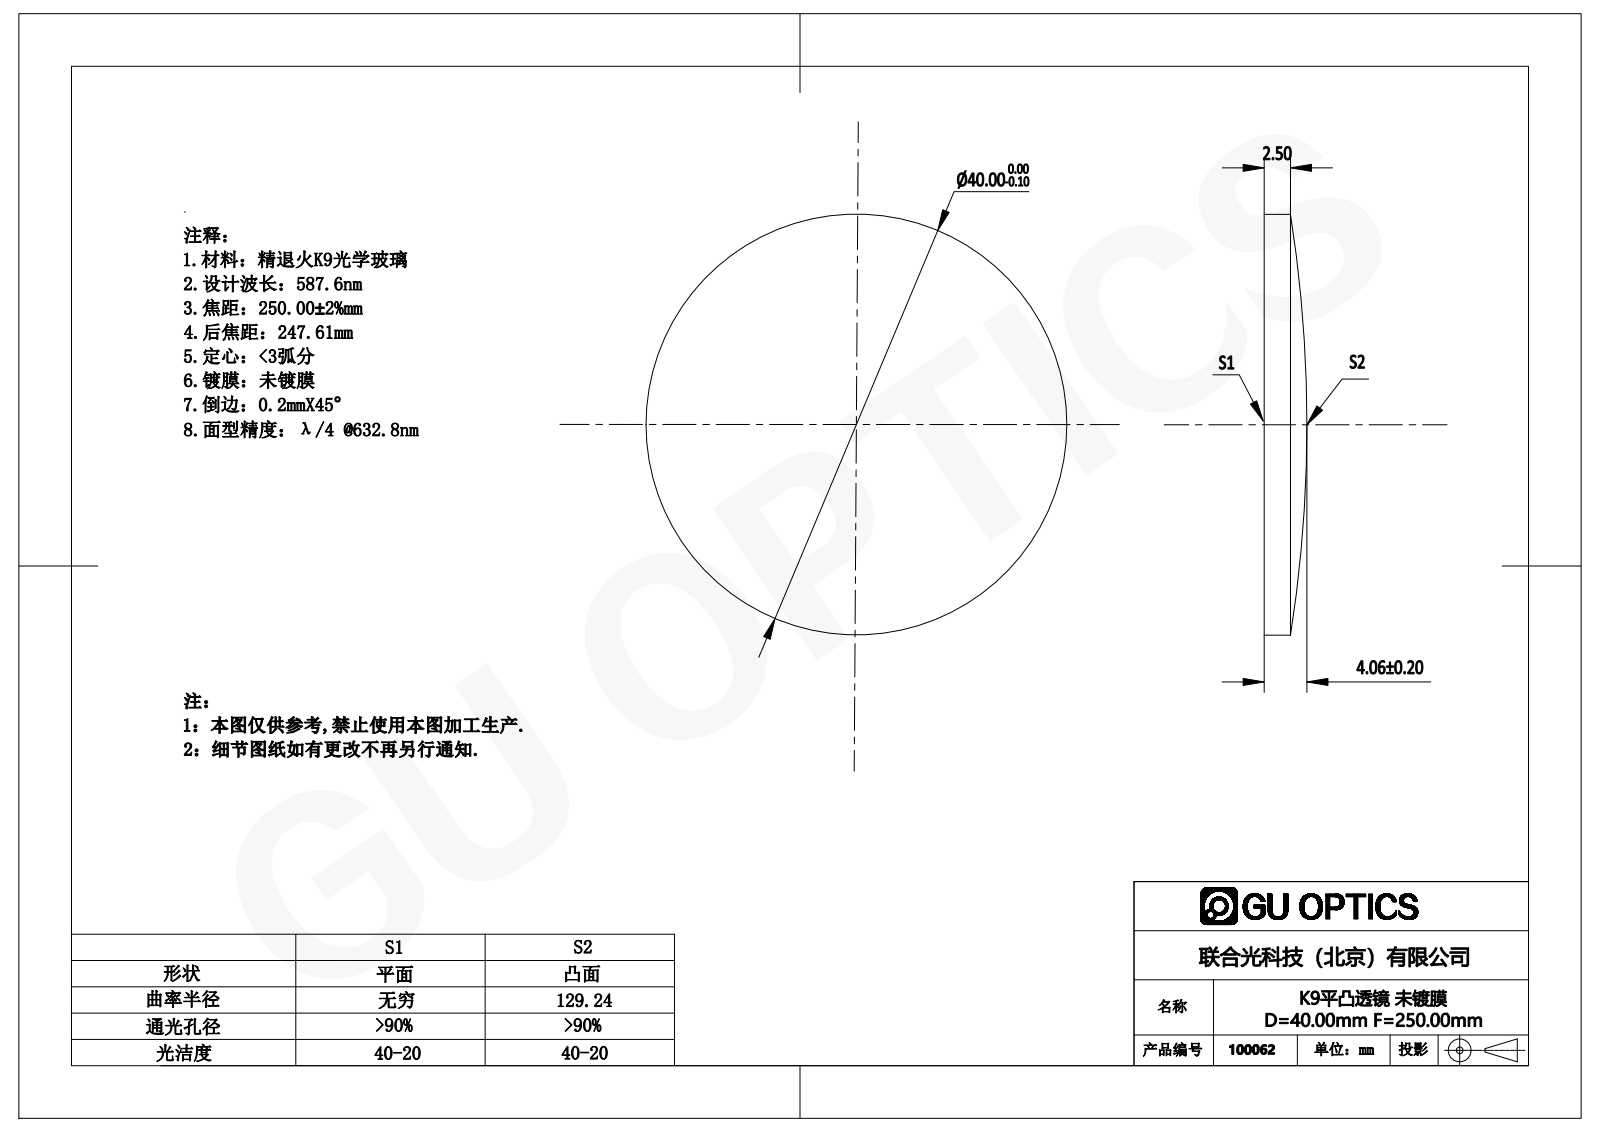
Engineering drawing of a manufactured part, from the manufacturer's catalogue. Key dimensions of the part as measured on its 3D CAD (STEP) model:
Part name (STEP PRODUCT): 100062
STEP written by: SolidWorks 2016 (AUTOMOTIVE_DESIGN)
Units: millimetres
Bodies: 1 solid, 5 faces (1 planar, 2 cylindrical, 2 other)
Overall size (bounding box): 40 × 40 × 4.06
Volume: 4 124 mm³ · Surface area: 2 835 mm²
Round bosses / shafts (diameter × count): ⌀40 ×1
